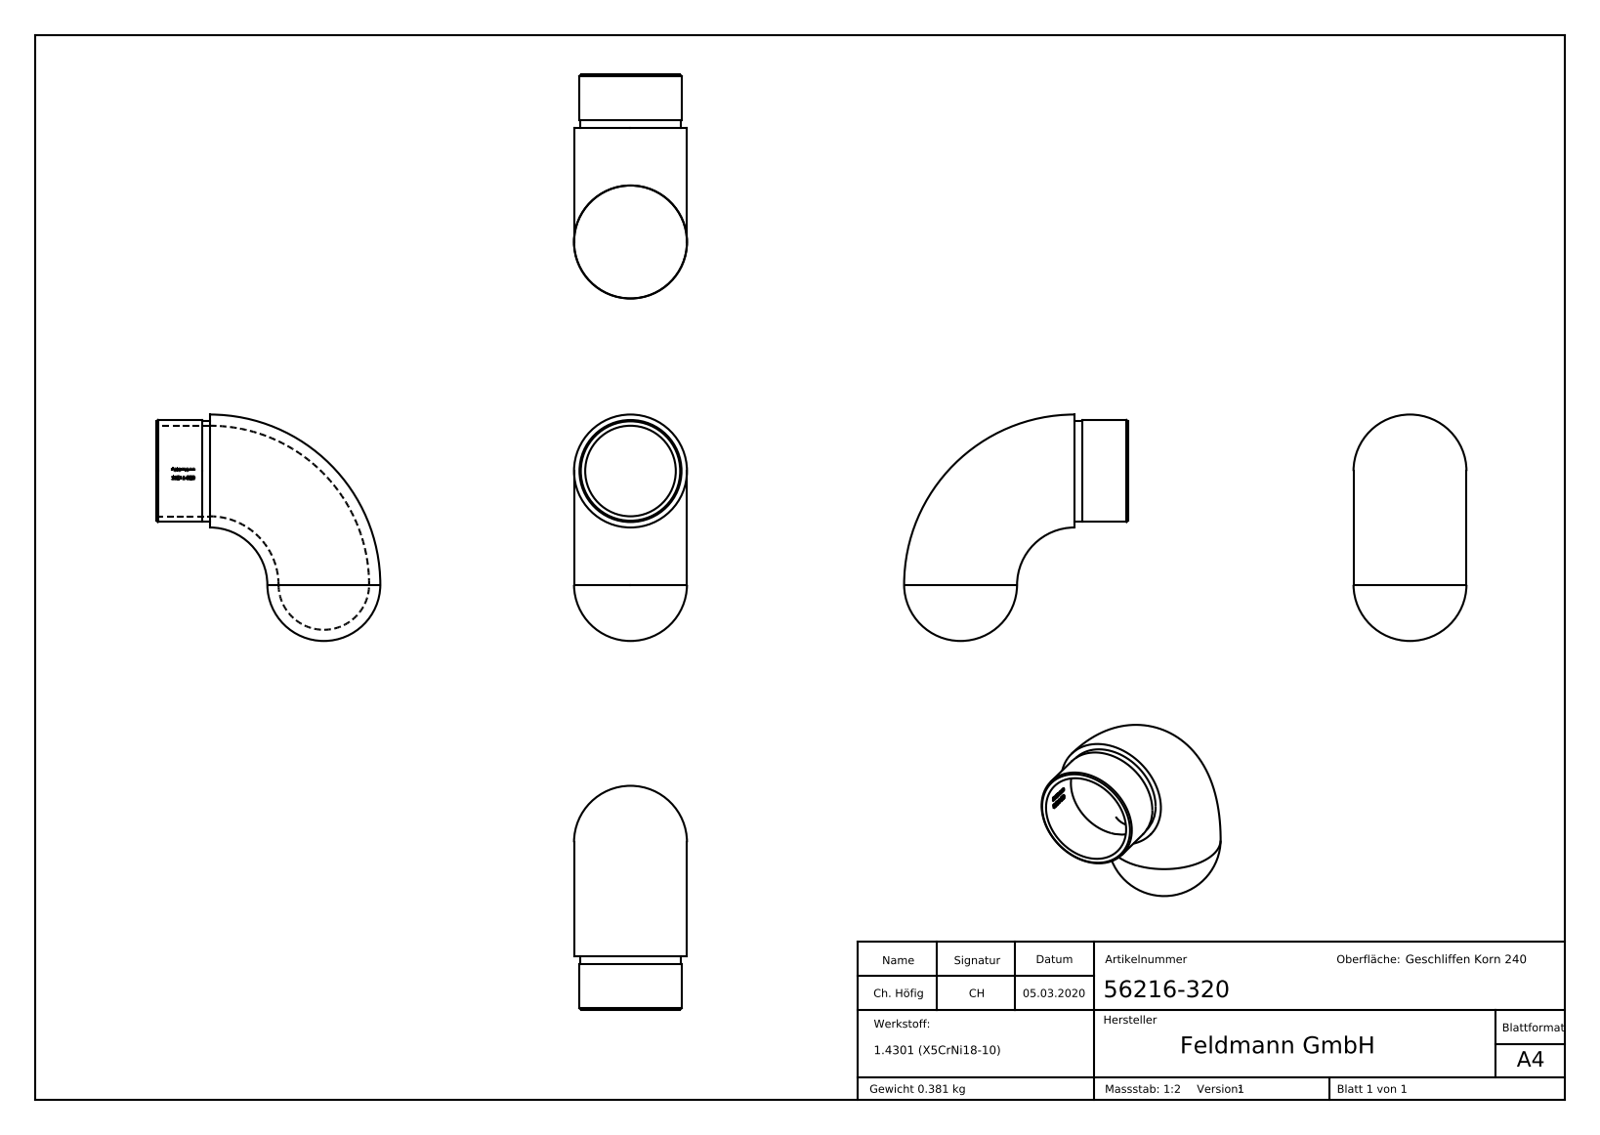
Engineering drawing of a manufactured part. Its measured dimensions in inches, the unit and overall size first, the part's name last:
Units: inches
Overall size (bounding box): 3.346 × 3.307 × 1.669
Round holes (diameter × count): ⌀1.339 ×1
Round bosses / shafts (diameter × count): ⌀1.508 ×1, ⌀1.492 ×1
Partial cylindrical surfaces — rounded edges, fillets, slot ends (radius × count): R0.673 ×1
Main face-to-face distances: 0.787, 0.118, 0.669, 0.139, 0.117, 0.134, 0.305, 0.015, 0.055, 0.052
Volume: 2.944 in³ · Surface area: 39.98 in²
Bodies: 1 solid, 236 faces (96 planar, 26 cylindrical, 114 other)
Part name (STEP PRODUCT): 56216-320
STEP written by: SolidWorks 2015 (CONFIG_CONTROL_DESIGN)
